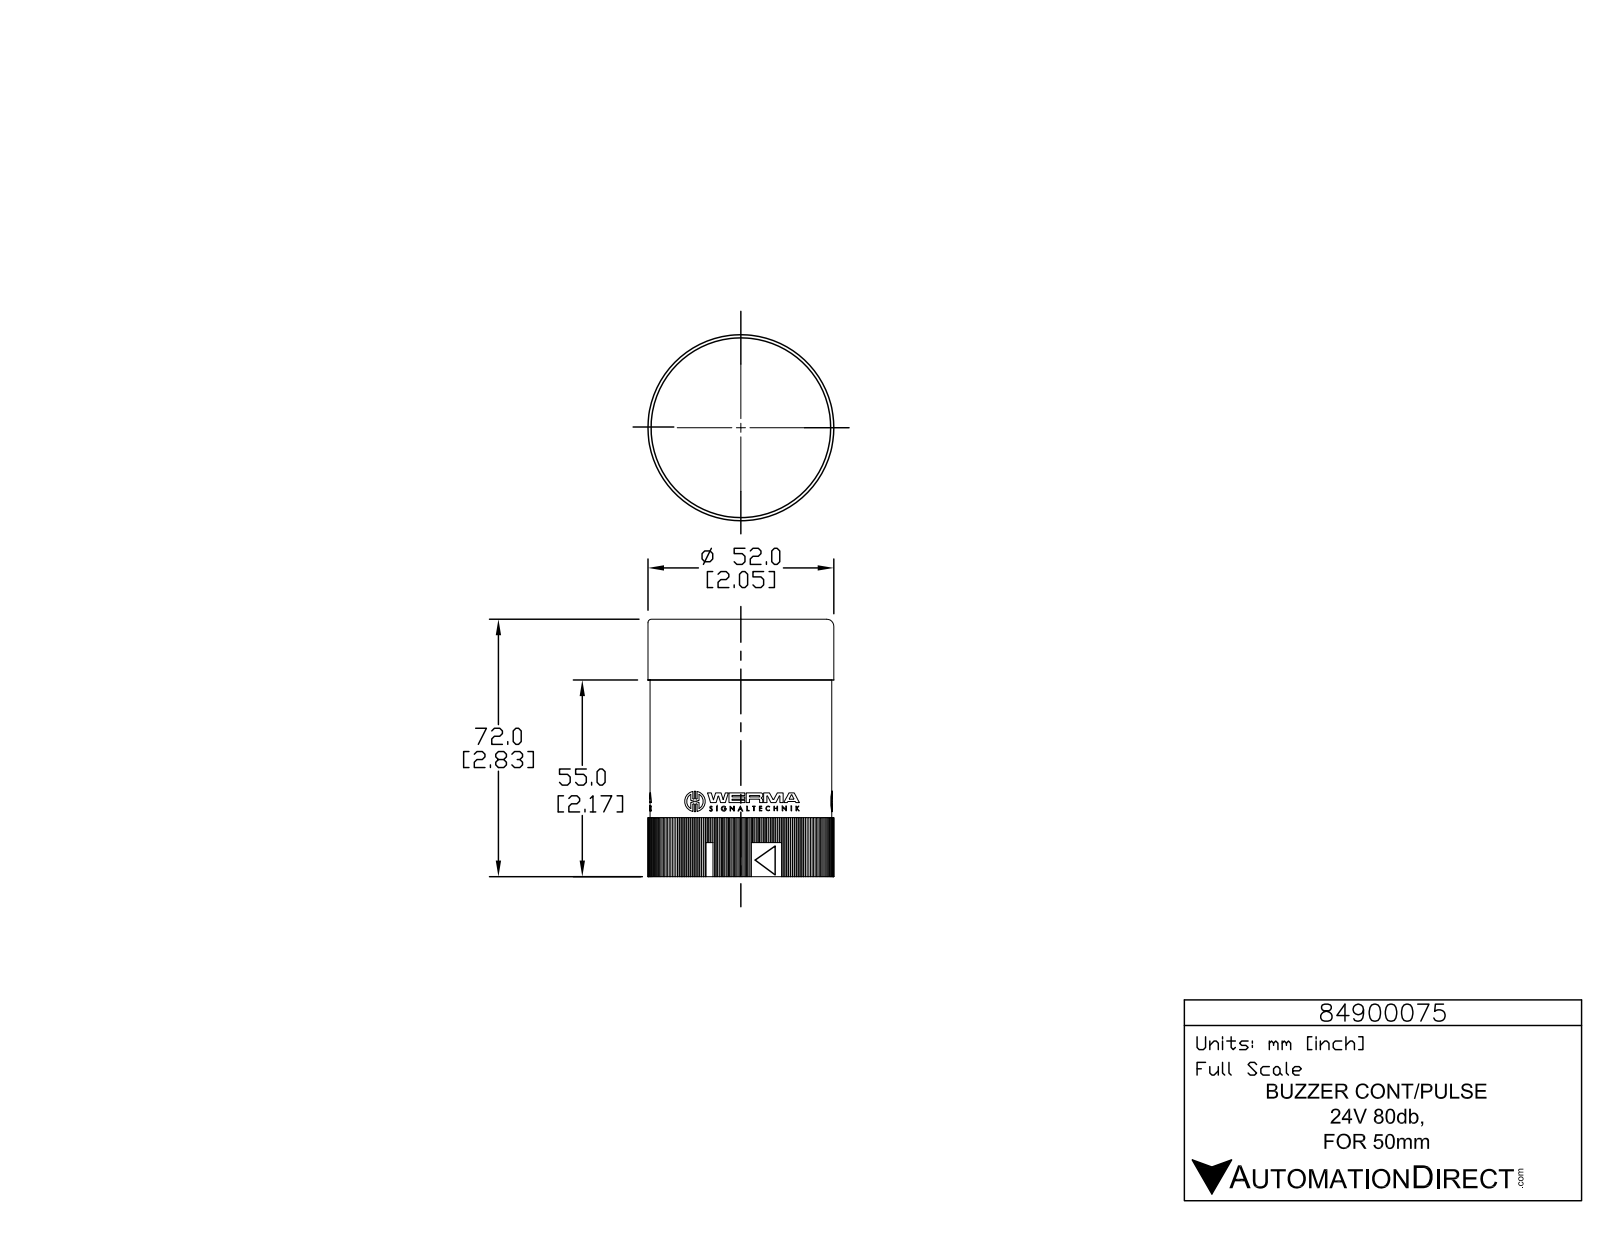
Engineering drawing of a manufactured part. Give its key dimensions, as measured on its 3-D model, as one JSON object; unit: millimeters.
{"part_name": "84900075", "step_written_by": "SolidWorks 2015 (AUTOMOTIVE_DESIGN)", "units": "millimeters", "bodies": {"solids": 1, "faces": 1267, "planar": 1020, "cylindrical": 245, "other": 2}, "overall_size": [72, 52, 52], "volume_mm3": 127000, "surface_area_mm2": 18890, "round_holes": [[1, 3], [48.2, 1]], "round_bosses_or_shafts": [[5.7, 3], [1.4, 3], [52, 1], [50.9, 1]], "partial_cylinders_radius": [[0.2, 6], [0.2, 6], [0.2, 6], [3.3, 6], [0.1, 3], [0.1, 3], [0.2, 3], [0.2, 3]], "face_to_face_distances": [60, 36.3, 36.3, 36.3, 72, 12, 36.3, 36.3, 17, 43]}
